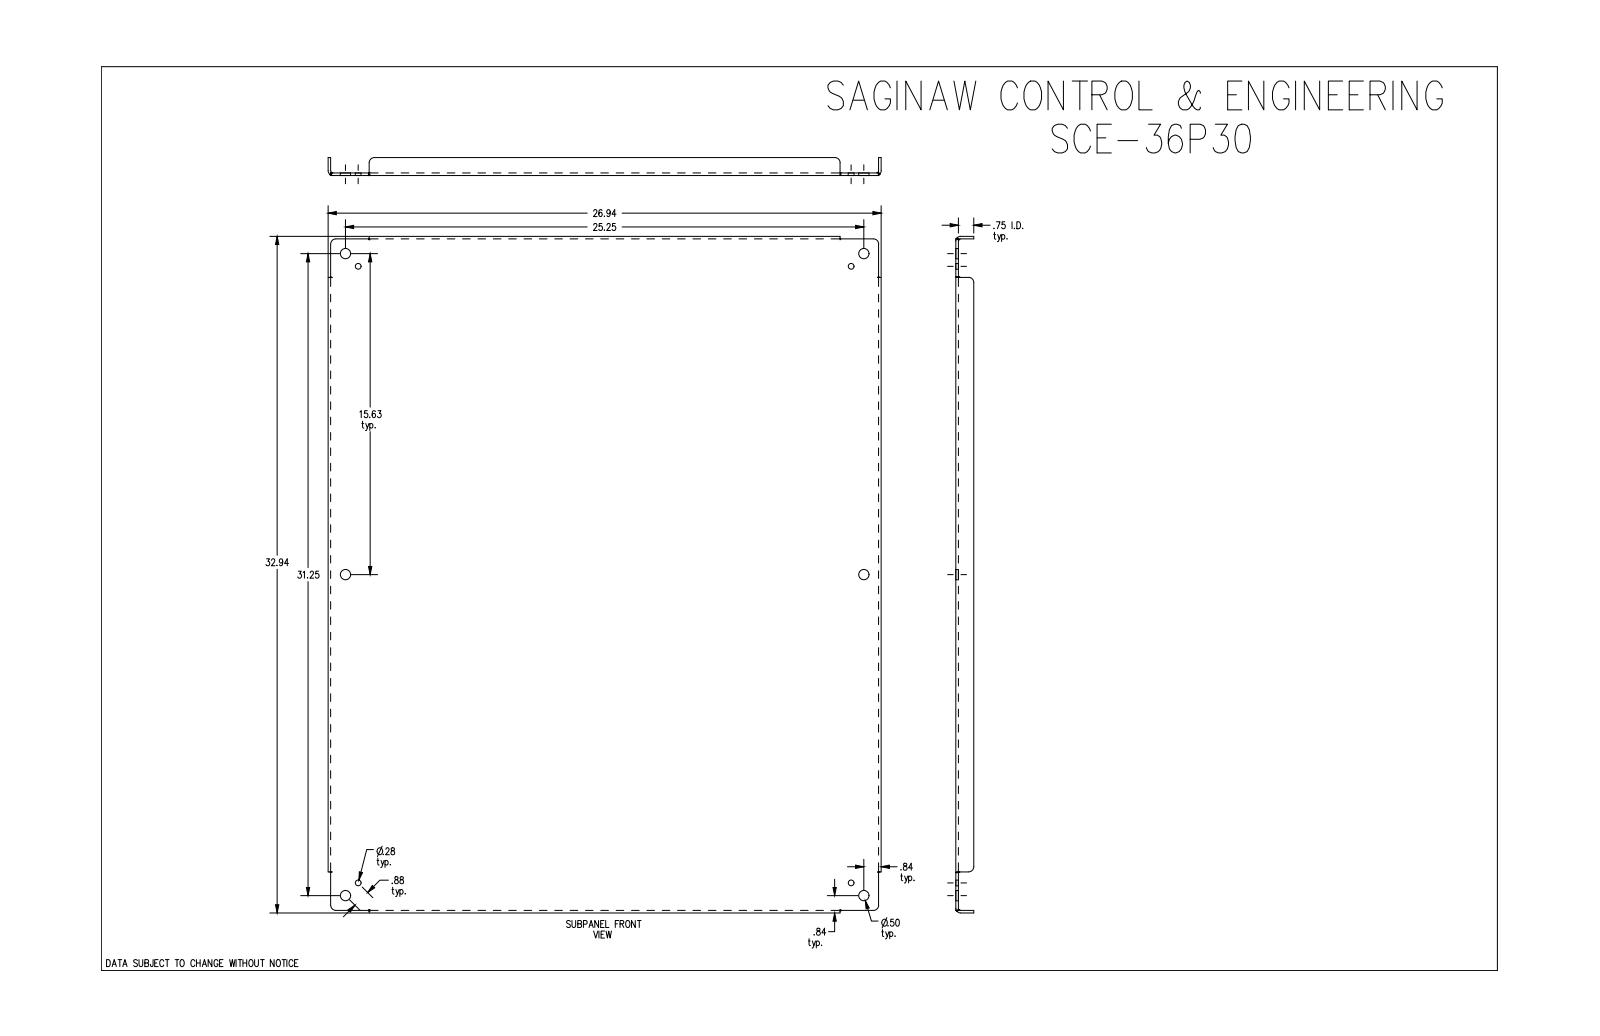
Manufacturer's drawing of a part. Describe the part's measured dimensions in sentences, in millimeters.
The part is named "SCE-36P30". Its 3-D file was written by "SolidWorks 2019 (CONFIG_CONTROL_DESIGN)". It is 1 solid with 84 faces: 30 planar, 30 cylindrical and 24 other. Overall it measures 836.6 by 684.2 by 22.2 millimeters. Its volume is 1 953 000 cubic millimeters and its surface area 1 242 000 square millimeters. Round holes: 6 of diameter 12.7, 4 of diameter 7.1. Partial cylindrical surfaces (rounded edges, fillets, slot ends): 8 of radius 6.4, 4 of radius 2.8, 4 of radius 6. The main face-to-face distances are 3.2, 3.2, 681.1, 833.5, 677.8, 684.2, 830.2, 836.6, 19.1, 22.2. The hole center spacings are 22.2, 381.5, 396.9, 625.8, 732.6, 754.2, 778.2, 998.4.
